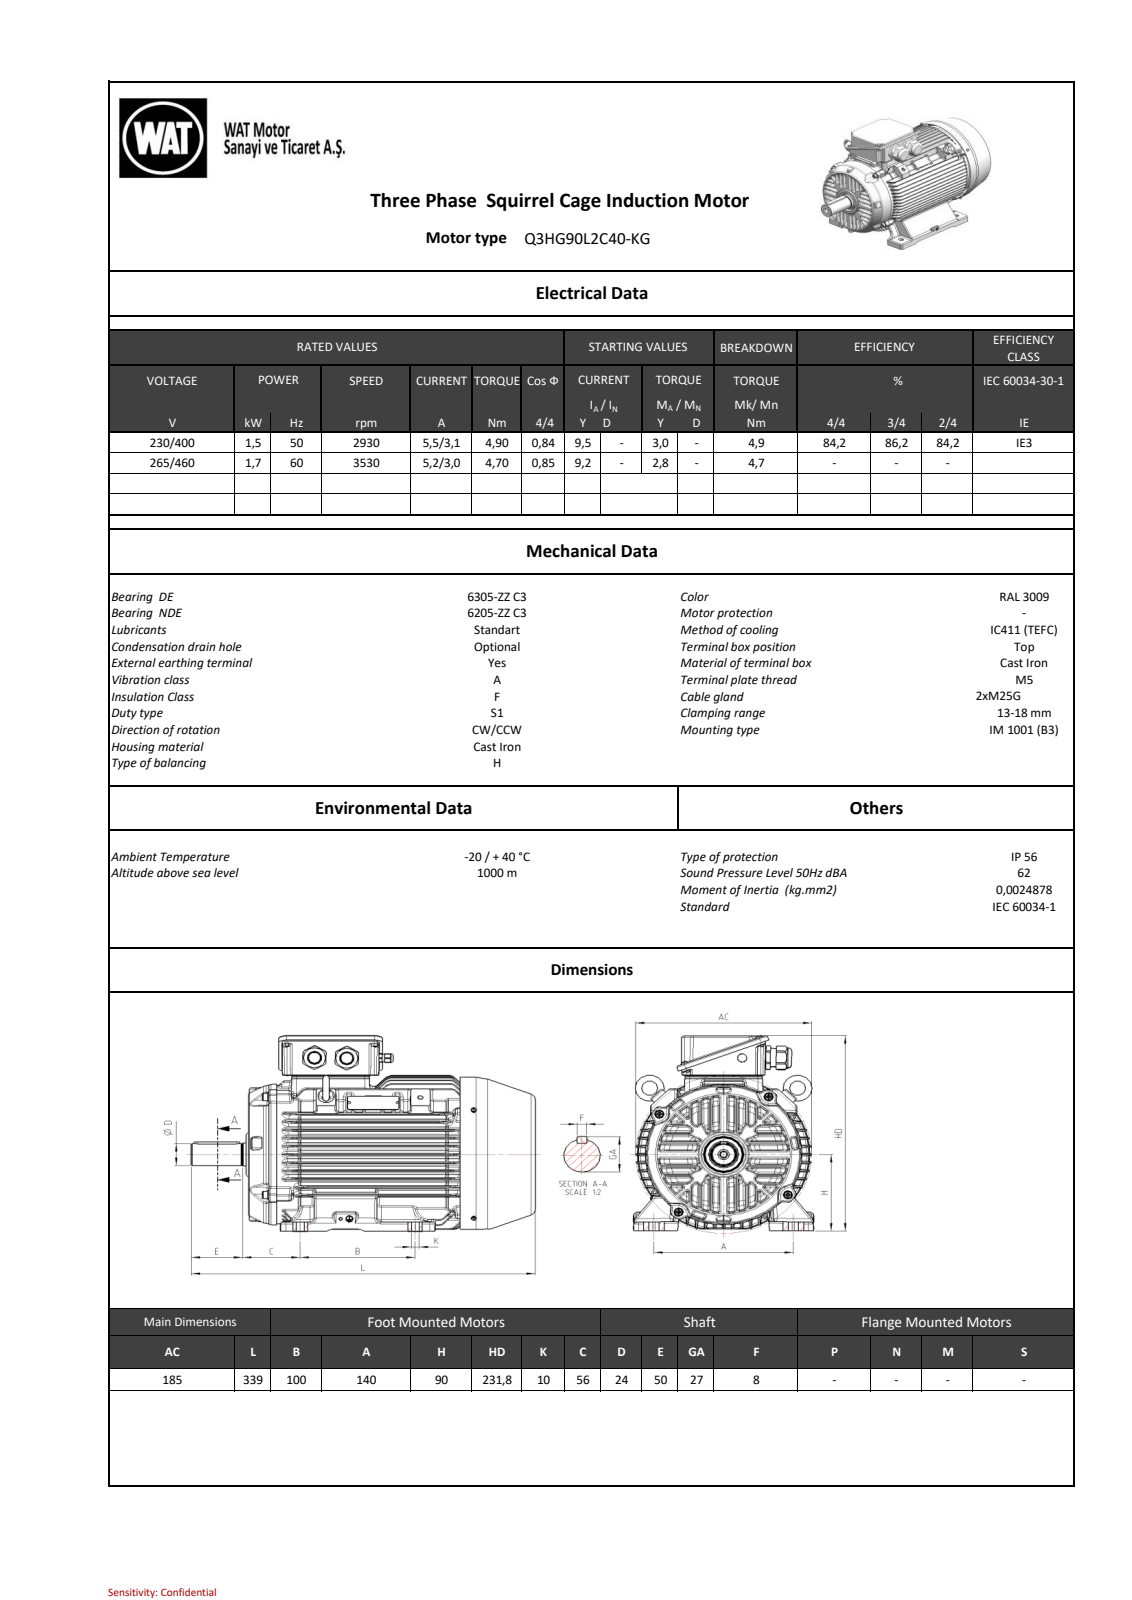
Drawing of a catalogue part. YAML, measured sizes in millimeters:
part_name: "C901B65877A5yis9"
step_written_by: "SIEMENS PLM Software NX 11.0 (AUTOMOTIVE_DESIGN)"
units: millimeters
bodies: {solids: 0, faces: 3170, planar: 878, cylindrical: 921, other: 1371}
overall_size: [338.47, 231.98, 226.53]
round_holes:
  - {diameter: 10, count: 3}
  - {diameter: 2.5, count: 2}
  - {diameter: 4.2, count: 2}
  - {diameter: 17.2, count: 2}
  - {diameter: 6.5, count: 1}
  - {diameter: 6.8, count: 1}
  - {diameter: 8.4, count: 1}
  - {diameter: 36.9, count: 1}
  - {diameter: 37.1, count: 1}
  - {diameter: 174, count: 1}
round_bosses_or_shafts:
  - {diameter: 20, count: 4}
  - {diameter: 8.65, count: 3}
  - {diameter: 8.5, count: 3}
  - {diameter: 8, count: 3}
  - {diameter: 5, count: 3}
  - {diameter: 27.7, count: 2}
  - {diameter: 25.25, count: 2}
  - {diameter: 9.2, count: 2}
partial_cylinders:
  - {radius: 1.5, count: 320}
  - {radius: 1, count: 43}
  - {radius: 2, count: 41}
  - {radius: 4, count: 32}
  - {radius: 5, count: 24}
  - {radius: 3, count: 12}
  - {radius: 26.5, count: 12}
  - {radius: 34.5, count: 12}
face_to_face_distances: [12.04, 49.79, 62.58, 3, 3.01, 281.32, 231.53, 1.5, 285.82, 236.03]
hole_center_spacings: [40, 75, 112.42]
